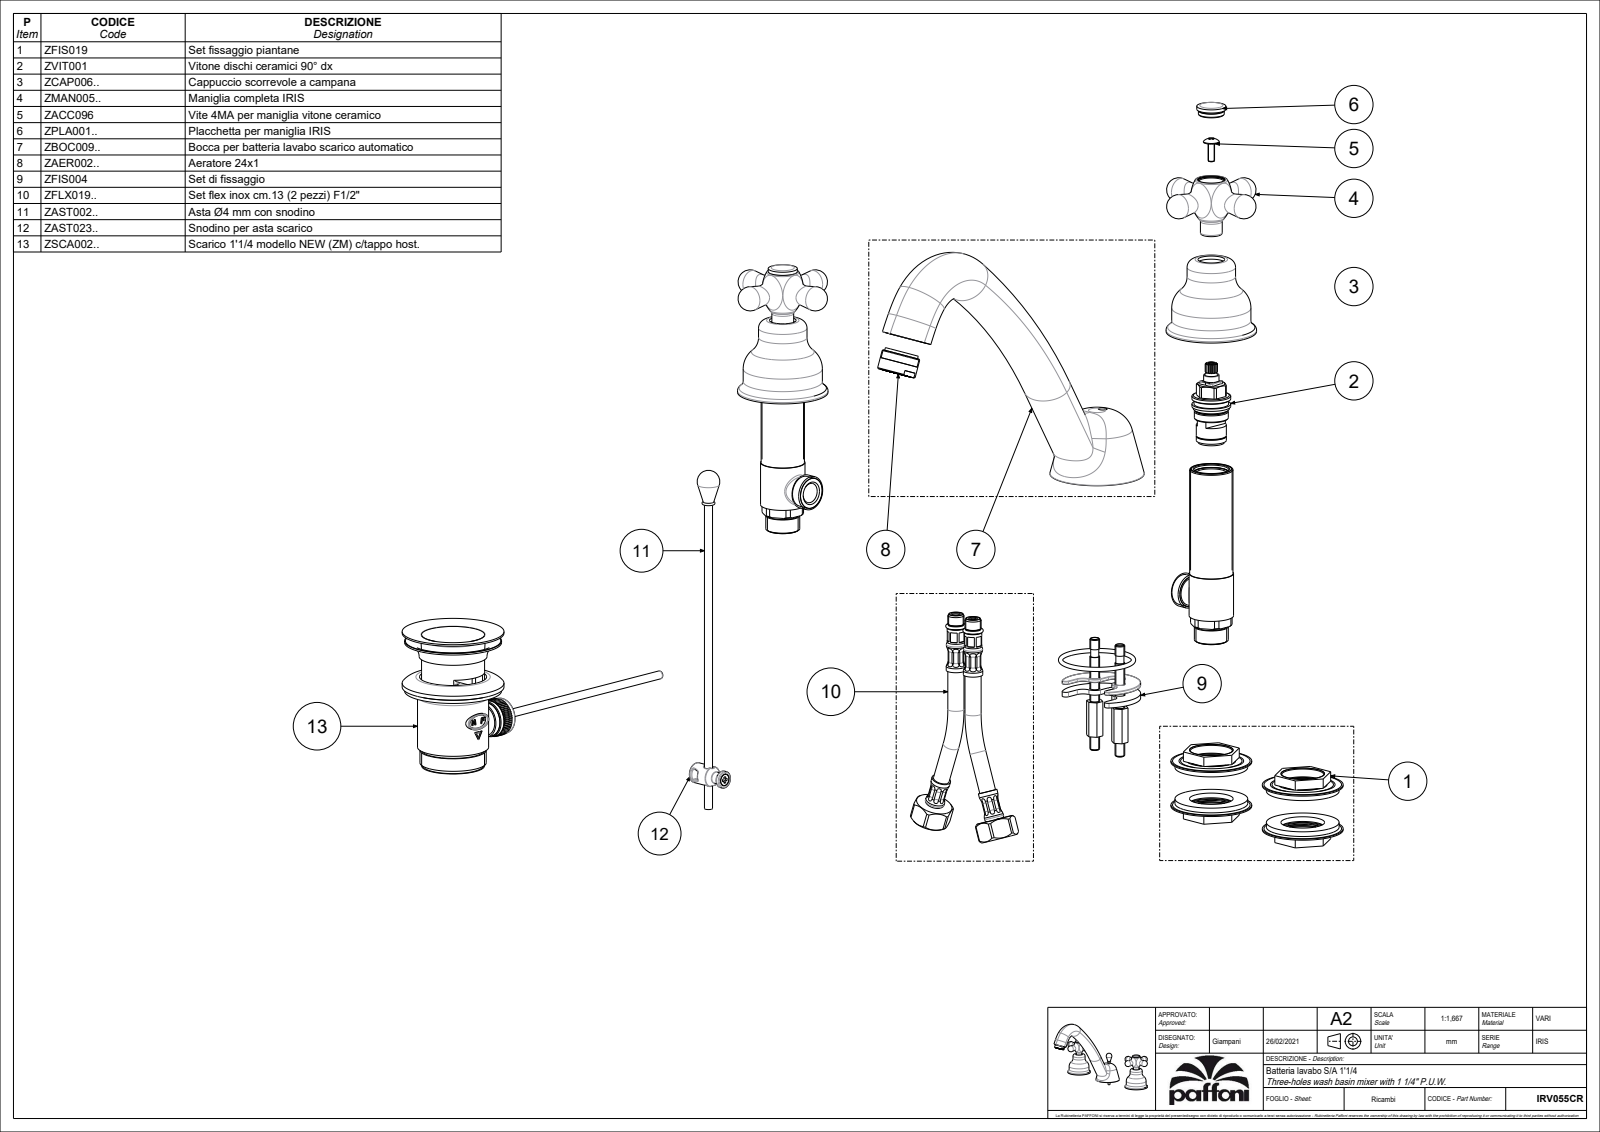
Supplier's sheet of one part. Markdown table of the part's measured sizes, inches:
| quantity | value |
| --- | --- |
| part name | IRV055CR |
| STEP written by | CREO PARAMETRIC BY PTC INC, 2020044 (CONFIG_CONTROL_DESIGN) |
| units | inches |
| bodies | 9 solids, 2177 faces (1575 planar, 261 cylindrical, 341 other) |
| overall size | 10.709 × 8.547 × 6.513 |
| volume | 14.18 in³ |
| surface area | 190 in² |
| round holes (diameter × count) | 0.217 × 3, 0.177 × 2, 0.346 × 2, 0.354 × 2, 0.406 × 2, 0.433 × 2, 0.63 × 2, 0.638 × 2, 0.642 × 2, 0.748 × 2, 1.012 × 2, 1.063 × 2 |
| round bosses / shafts (diameter × count) | 0.945 × 3, 0.197 × 3, 2.165 × 2, 1.929 × 2, 1.161 × 2, 1.102 × 2, 1.055 × 2, 0.843 × 2 |
| partial cylindrical surfaces (radius × count) | 0.004 × 34, 0.039 × 12, 0.098 × 8, 0.031 × 5, 0.02 × 4, 0.197 × 2, 0.37 × 2, 0.736 × 1 |
| main face-to-face distances | 0.118, 0.031, 0.15, 0.047, 0.02, 0.323, 0.157, 0.276, 0.205, 0.138 |
| hole center spacings | 0.378, 0.461, 0.524, 0.559, 0.606, 0.938, 3.522, 3.649 |
